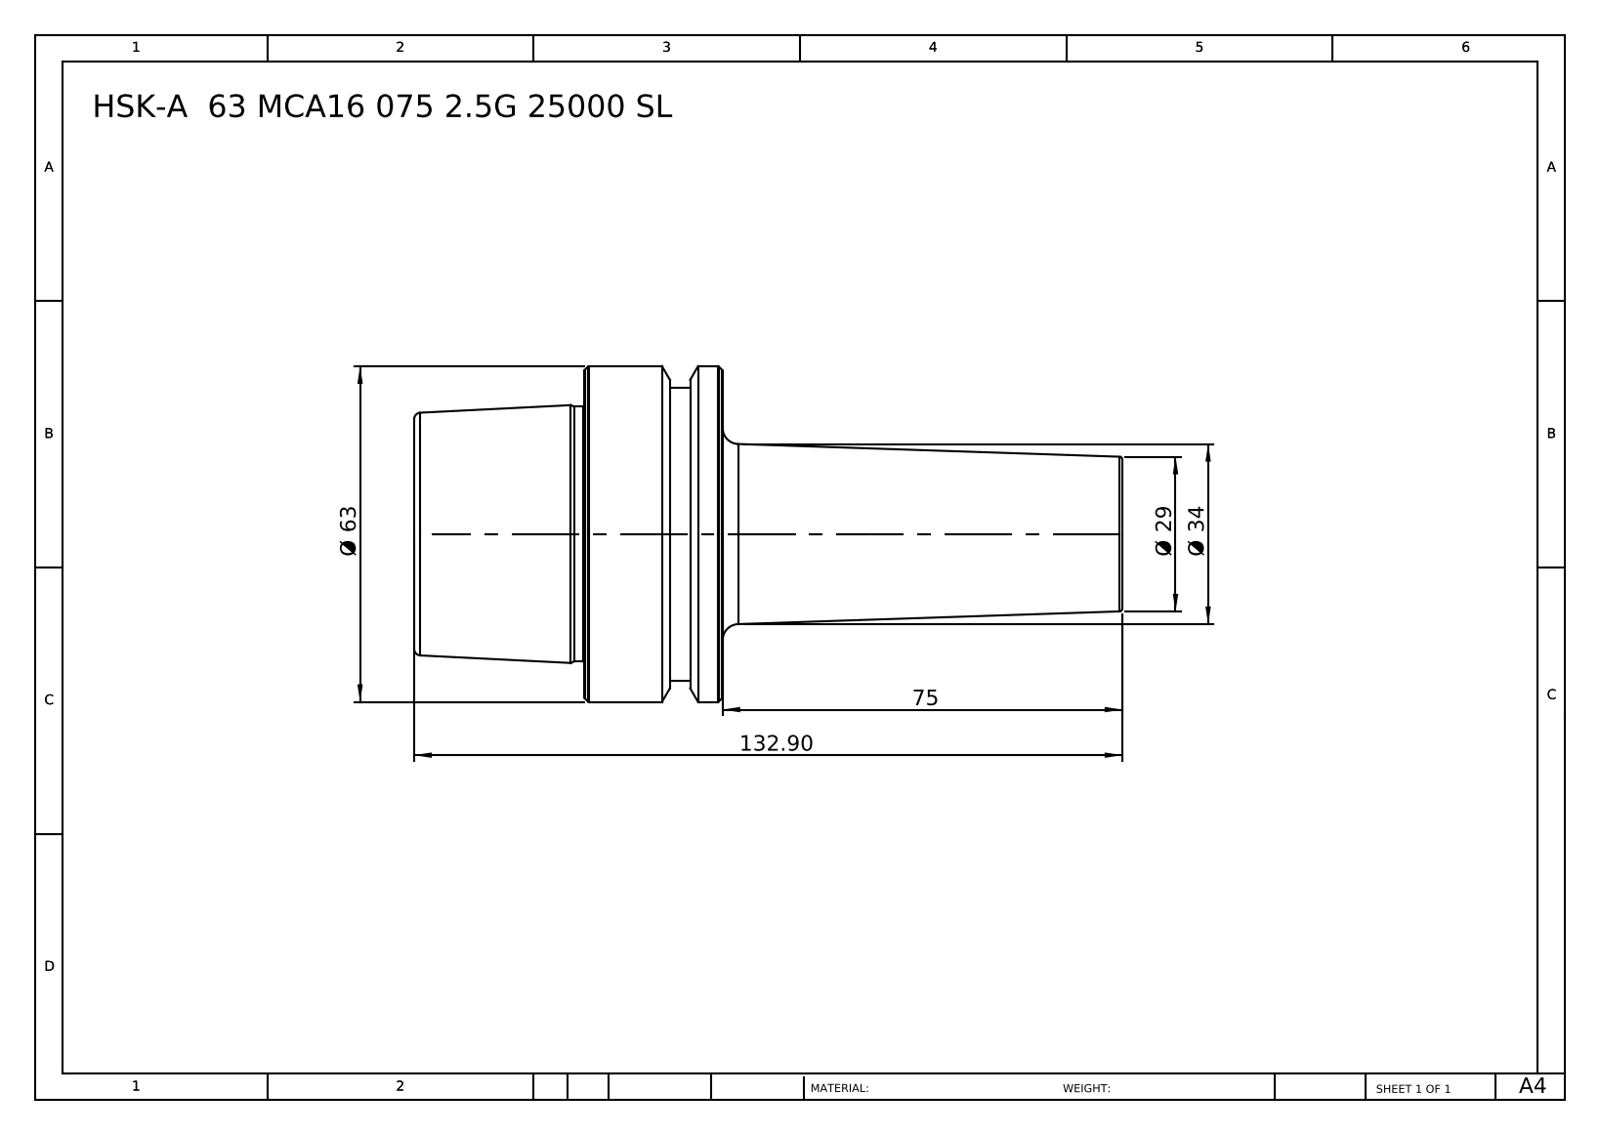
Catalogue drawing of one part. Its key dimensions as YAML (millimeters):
part_name: "HSK-A 63 MCA16 075 2.5G 25000 SL"
step_written_by: "SolidWorks 2014 (CONFIG_CONTROL_DESIGN)"
units: millimeters
bodies: {solids: 1, faces: 46, planar: 6, cylindrical: 8, other: 32}
overall_size: [132.9, 63, 63]
volume: 191360
surface_area: 23686
round_bosses_or_shafts:
  - {diameter: 63, count: 1}
  - {diameter: 55, count: 1}
  - {diameter: 47.78, count: 1}
face_to_face_distances: [57.9, 26, 31.9, 75, 101, 132.9, 81.1, 6.1, 19.9, 51.8]
